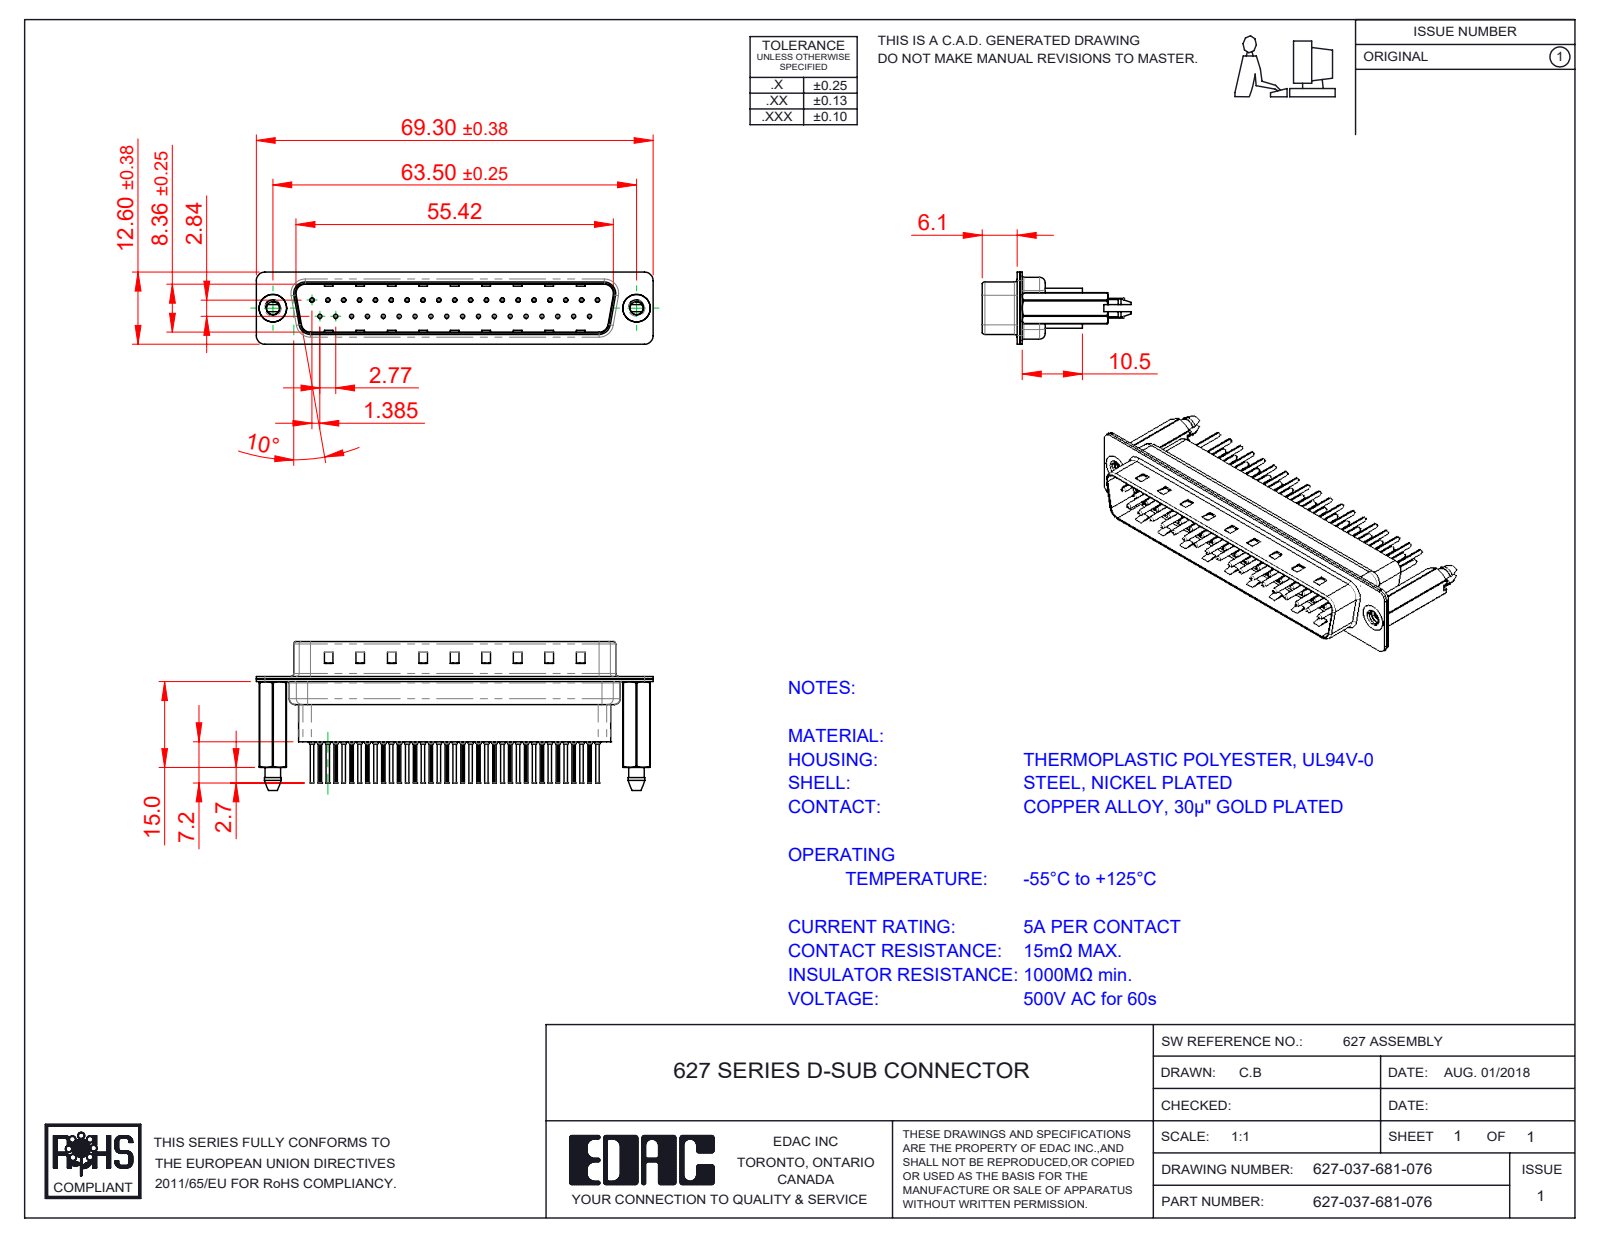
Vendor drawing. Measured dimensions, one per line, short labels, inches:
name: 627 Housing_37 HP; 627 Shell Rear_37 Contacts; 627 4-40 Threaded Boardlock_HP81; 627-037-681-076 (+3 more)
written by: SolidWorks 2020 (CONFIG_CONTROL_DESIGN)
unit: in
bodies: 42 solids, 4146 faces (1123 planar, 1576 cylindrical, 1447 other)
size: 2.728 × 1.02 × 0.496
volume: 0.349 in³; area: 22.85 in²
holes: 37× ⌀0.008, 37× ⌀0.014, 37× ⌀0.043, 37× ⌀0.063, 2× ⌀0.089, 2× ⌀0.157, 2× ⌀0.189
bosses: 37× ⌀0.079, 37× ⌀0.059, 37× ⌀0.03, 37× ⌀0.024, 2× ⌀0.193
rounds: 74× R0.004, 18× R0.059, 12× R0.079, 10× R0.063, 8× R0.02, 4× R0.01, 4× R0.024, 4× R0.026
face distances: 0.016, 0.032, 0.377, 0.027, 0.302, 0.018, 0.059, 0.043, 0.318, 0.345
hole spacings: 0.124, 0.109, 0.218, 0.327, 0.198, 0.398, 0.436, 0.503
